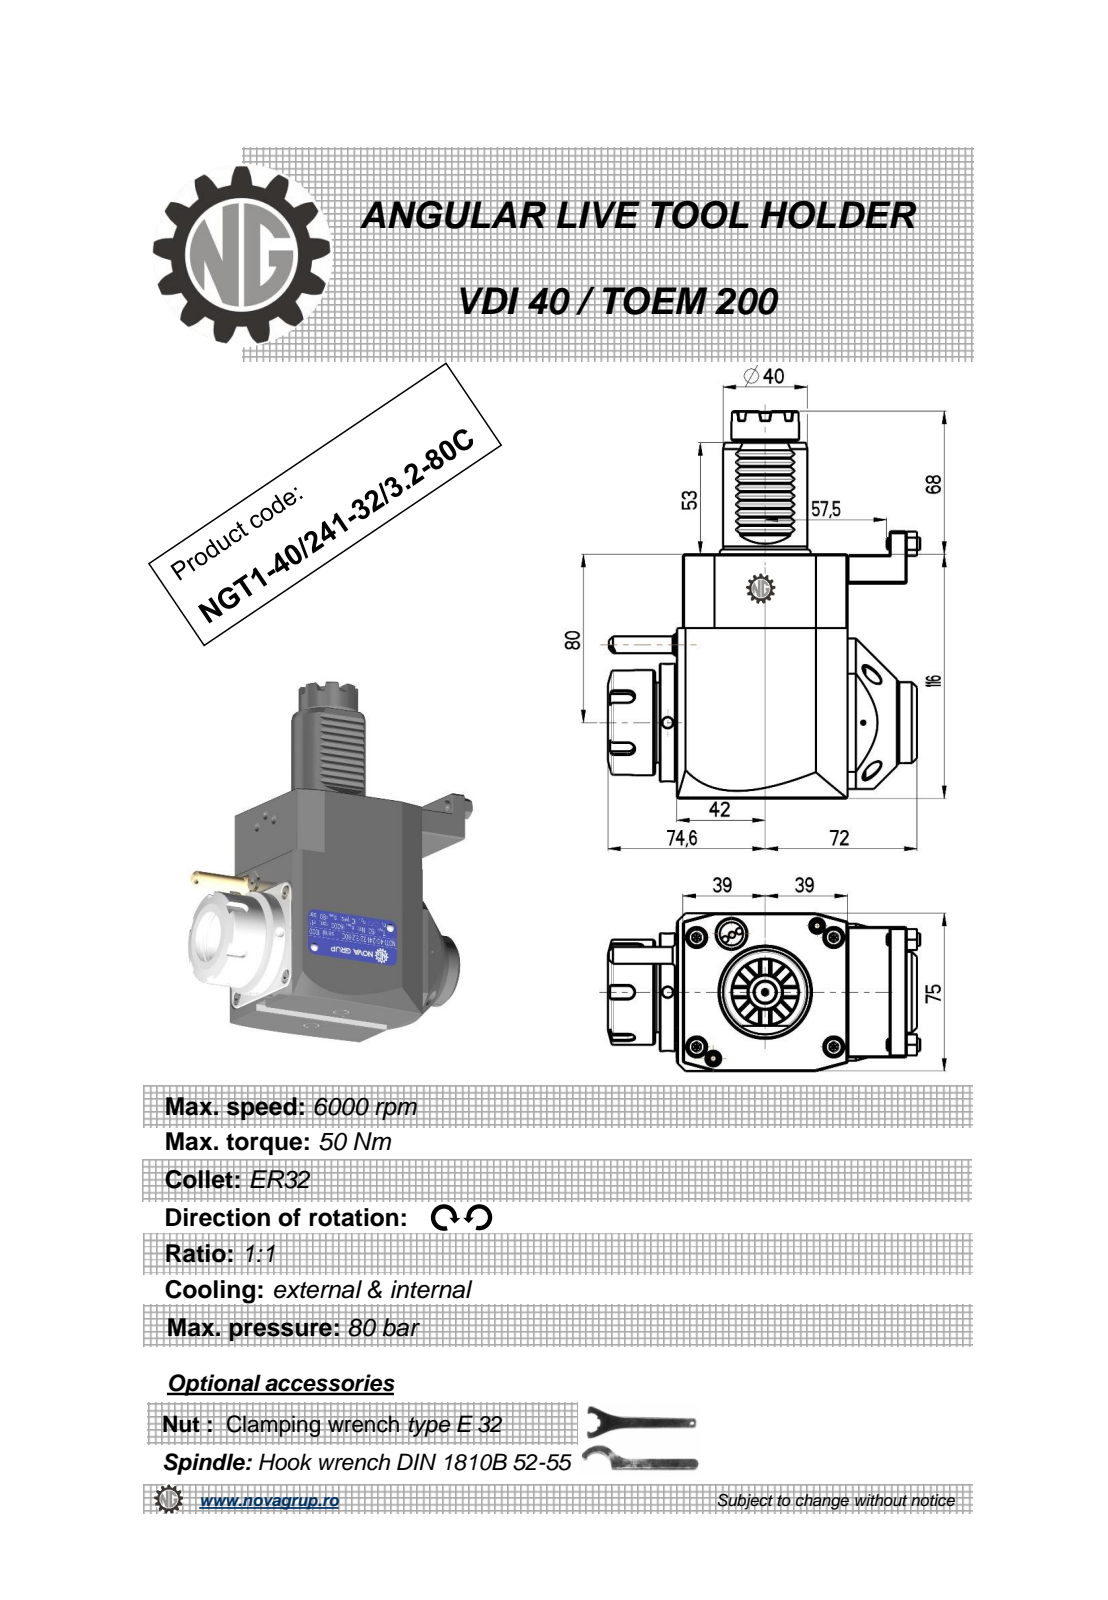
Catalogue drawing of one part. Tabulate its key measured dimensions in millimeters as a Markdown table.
| quantity | value |
| --- | --- |
| part name | NGT1_40_241_32_3_2_80C |
| STEP written by | PRO/ENGINEER BY PARAMETRIC TECHNOLOGY CORPORATION, 2010280 (CONFIG_CONTROL_DESIGN) |
| units | millimeters |
| bodies | 1 solid, 479 faces (214 planar, 79 cylindrical, 186 other) |
| overall size | 184 × 148.1 × 75 |
| volume | 929 999 mm³ |
| surface area | 76 611 mm² |
| round holes (diameter × count) | 5 × 3, 3 × 1, 27 × 1 |
| round bosses / shafts (diameter × count) | 6 × 2, 56 × 1, 50 × 1, 43 × 1, 40 × 1, 38.5 × 1, 32 × 1, 17.2 × 1 |
| partial cylindrical surfaces (radius × count) | 0.3 × 10, 0.31 × 10, 0.2 × 6, 3 × 5, 0.5 × 1, 40 × 1 |
| main face-to-face distances | 75, 116, 0.5, 81, 78, 3, 109, 14, 102, 11 |
| hole center spacings | 40.93 |
